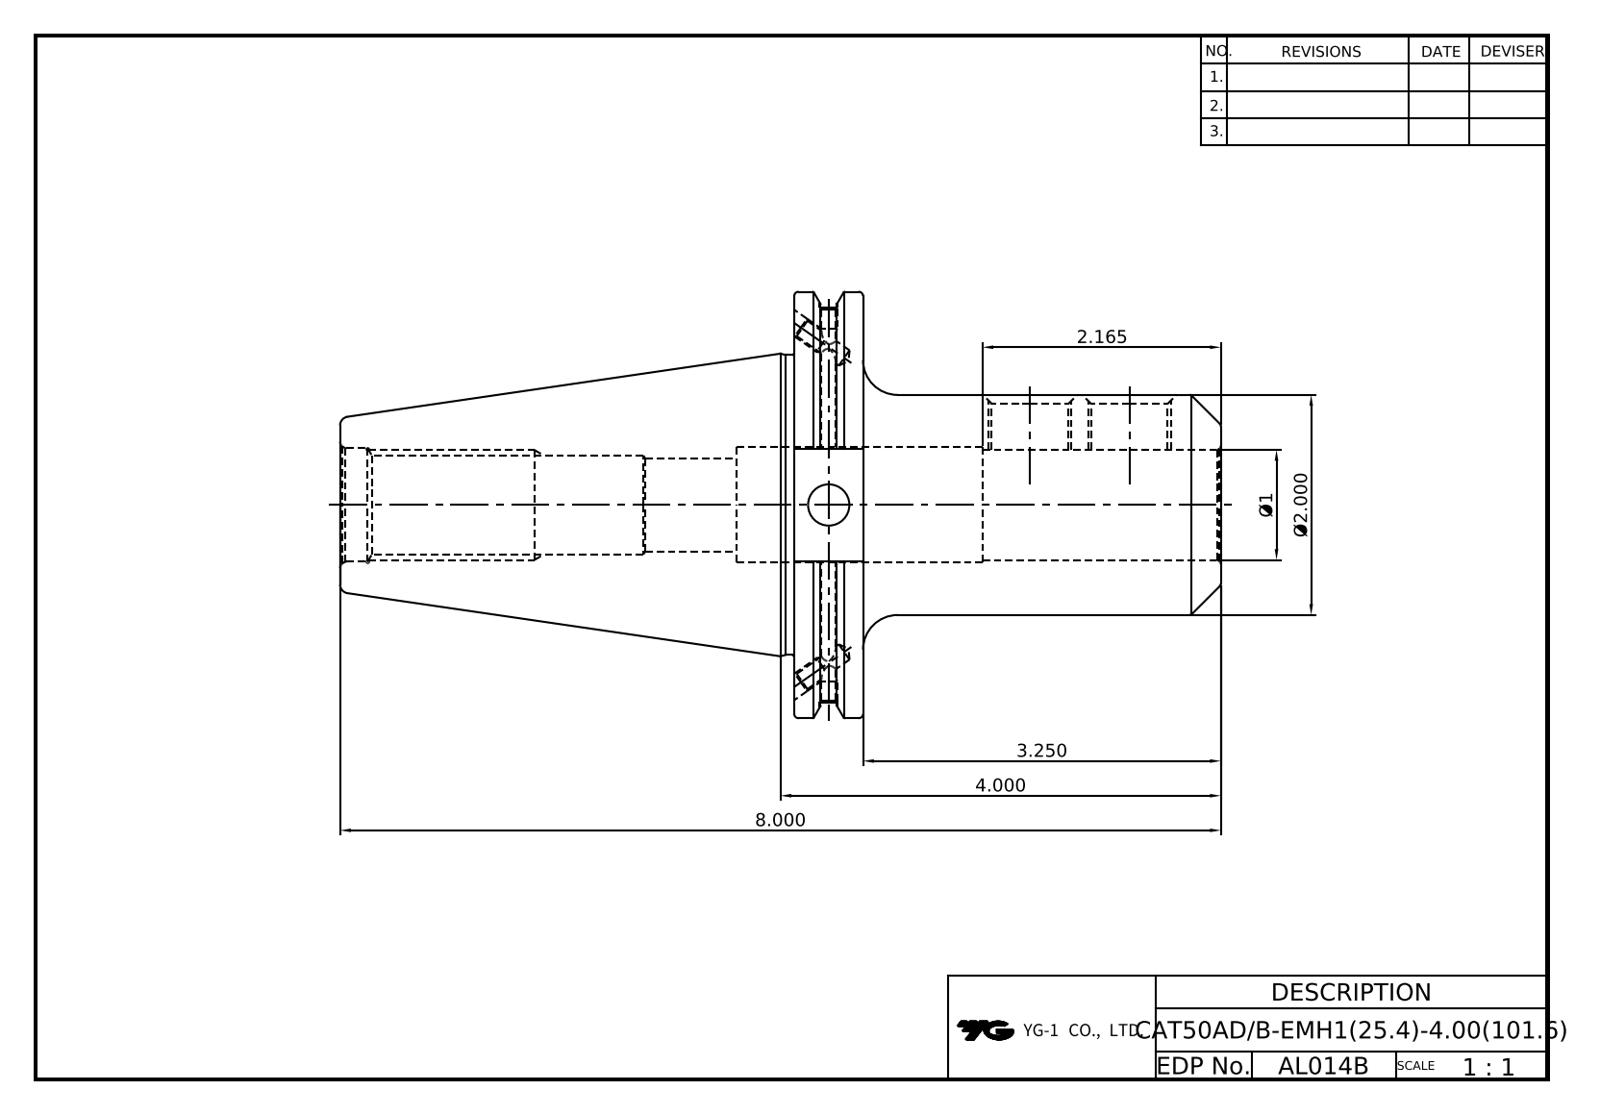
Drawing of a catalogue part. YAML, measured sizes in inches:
part_name: "LO-CAT50ADB-EMH25.4-101.6"
step_written_by: "Autodesk Inventor 2022 (AUTOMOTIVE_DESIGN)"
units: inches
bodies: {solids: 1, faces: 91, planar: 39, cylindrical: 28, other: 24}
overall_size: [8, 3.875, 3.728]
volume: 26.23
surface_area: 99.45
round_holes:
  - {diameter: 0.128, count: 2}
  - {diameter: 0.163, count: 2}
  - {diameter: 0.165, count: 2}
  - {diameter: 0.197, count: 2}
  - {diameter: 0.682, count: 2}
  - {diameter: 0.375, count: 1}
  - {diameter: 0.846, count: 1}
  - {diameter: 0.865, count: 1}
  - {diameter: 1, count: 1}
  - {diameter: 1.031, count: 1}
  - {diameter: 1.047, count: 1}
round_bosses_or_shafts:
  - {diameter: 3.875, count: 1}
  - {diameter: 3.594, count: 1}
  - {diameter: 2.726, count: 1}
  - {diameter: 2, count: 1}
face_to_face_distances: [0.625, 4.125, 4.75, 8, 3.875, 3.25, 2.875, 1.02, 3.603, 0.522]
hole_center_spacings: [0.902]
